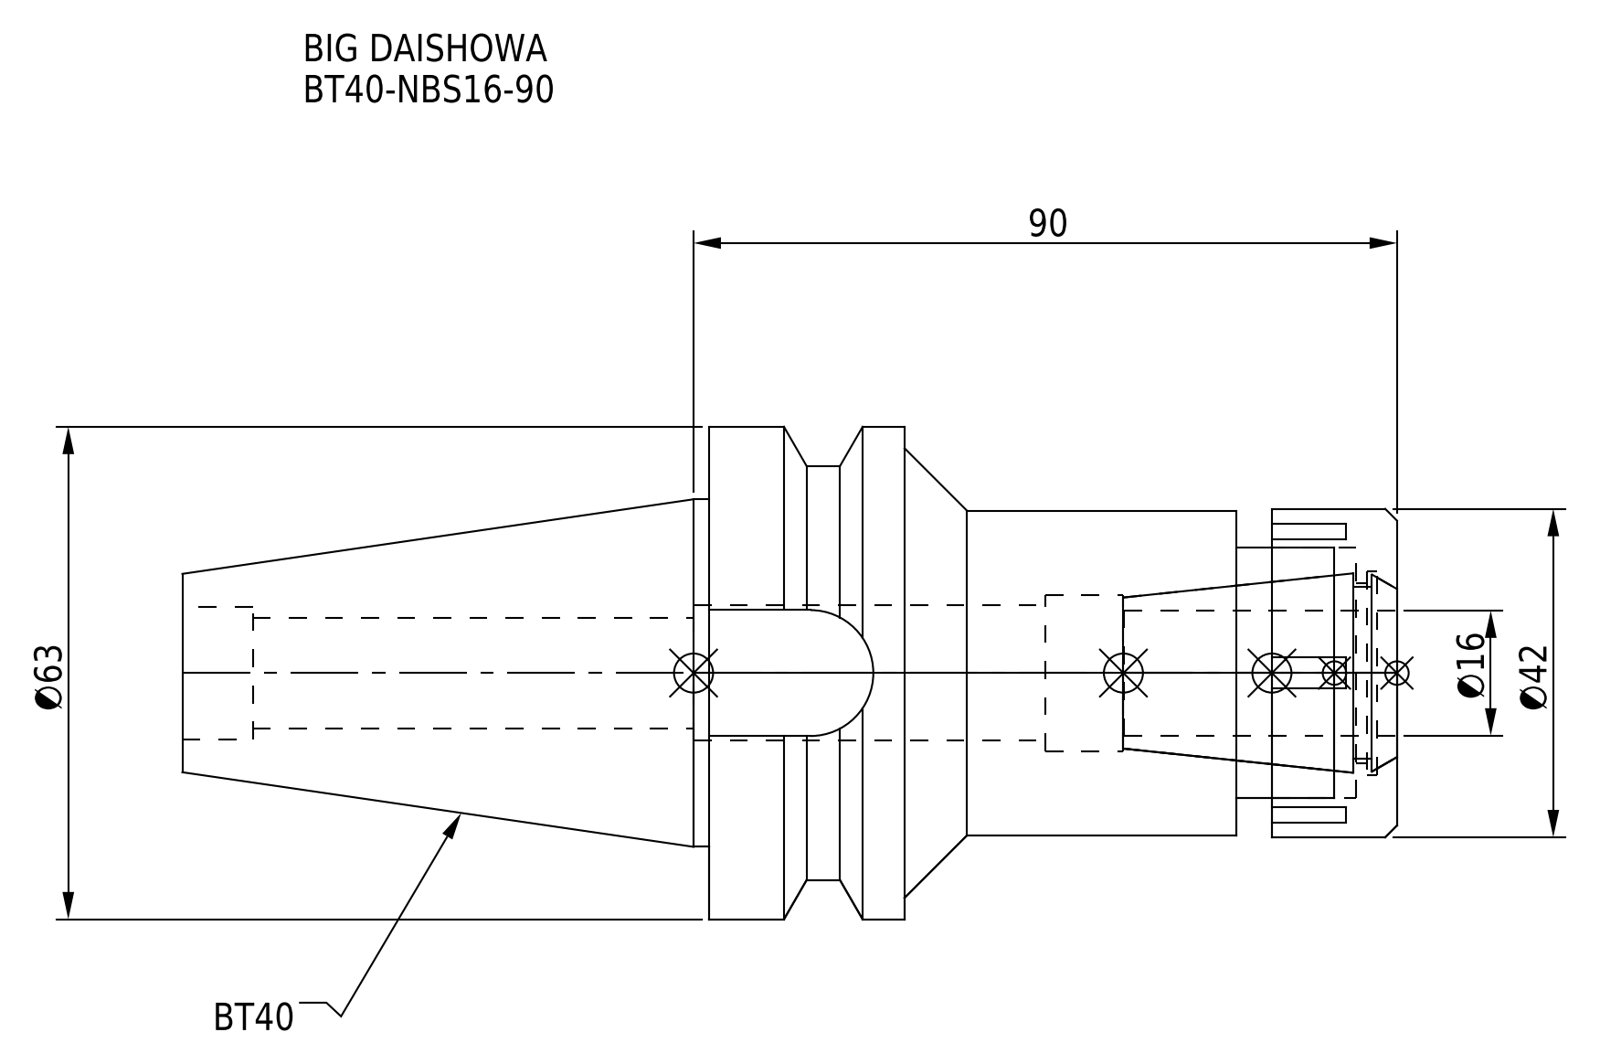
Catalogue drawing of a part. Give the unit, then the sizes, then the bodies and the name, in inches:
Units: inches
Overall size (bounding box): 6.118 × 2.48 × 2.48
Round holes (diameter × count): ⌀0.559 ×1, ⌀0.669 ×1, ⌀0.681 ×1, ⌀0.787 ×1, ⌀0.906 ×1, ⌀1.024 ×1, ⌀1.26 ×1
Round bosses / shafts (diameter × count): ⌀2.48 ×1, ⌀2.087 ×1, ⌀1.75 ×1, ⌀1.654 ×1, ⌀1.634 ×1
Partial cylindrical surfaces — rounded edges, fillets, slot ends (radius × count): R0.317 ×1
Main face-to-face distances: 3.465, 0.315, 0.807, 2.657, 0.63, 0.177, 2.835, 2.48, 1.85, 1.673
Volume: 11.1 in³ · Surface area: 59.54 in²
Bodies: 2 solids, 88 faces (44 planar, 30 cylindrical, 14 other)
Part name (STEP PRODUCT): DXF_TEMP_ASSY_ASM_4_ASM.stp; BT40-NBS16-90-FreeParts; BT40NB16090-160_ASM.stp; NBN16_1.stp (+3 more)
STEP written by: SolidWorks 2019 (CONFIG_CONTROL_DESIGN)
